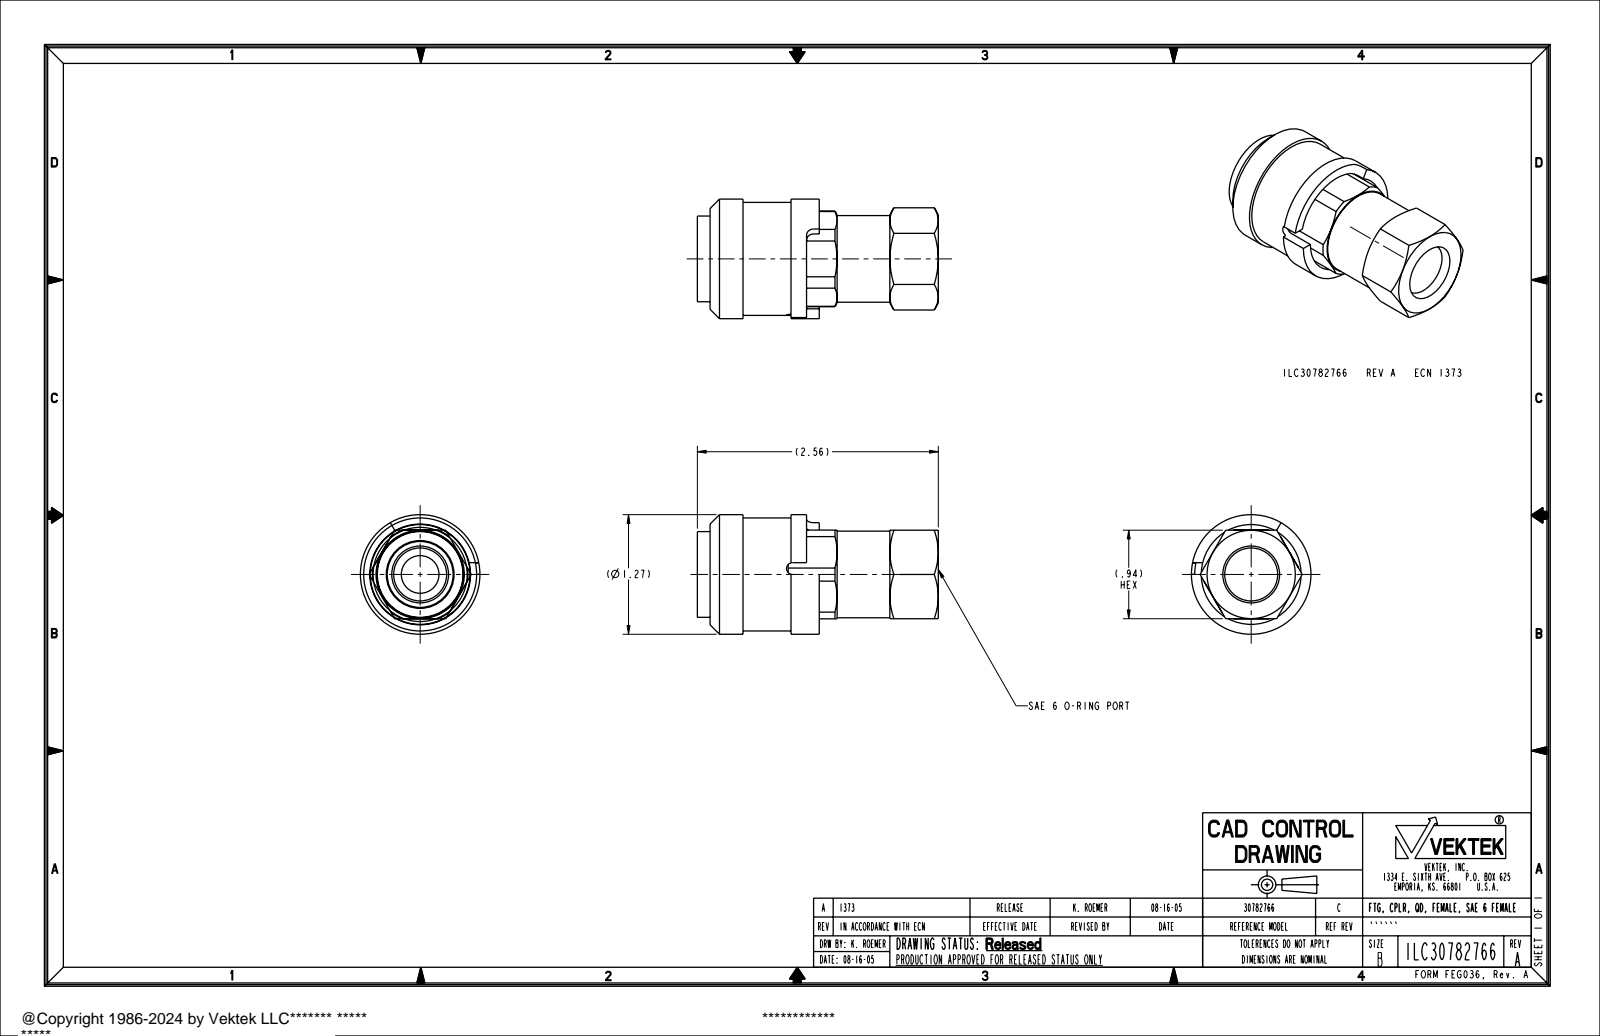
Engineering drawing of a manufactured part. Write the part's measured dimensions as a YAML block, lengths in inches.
part_name: "ILC30782766"
step_written_by: "PRO/ENGINEER BY PARAMETRIC TECHNOLOGY CORPORATION, 2004290 (AUTOMOTIVE_DESIGN_CC2)"
units: inches
bodies: {solids: 1, faces: 69, planar: 28, cylindrical: 27, other: 14}
overall_size: [2.56, 1.27, 1.27]
volume: 1.849
surface_area: 16.75
round_holes:
  - {diameter: 0.4, count: 1}
  - {diameter: 0.563, count: 1}
  - {diameter: 0.7, count: 1}
  - {diameter: 1, count: 1}
  - {diameter: 1.06, count: 1}
round_bosses_or_shafts:
  - {diameter: 1.27, count: 1}
  - {diameter: 1.2, count: 1}
  - {diameter: 0.92, count: 1}
  - {diameter: 0.91, count: 1}
partial_cylinders:
  - {radius: 0.062, count: 1}
  - {radius: 0.075, count: 1}
  - {radius: 0.508, count: 1}
face_to_face_distances: [0.94, 0.941, 0.943, 0.485, 1.265, 0.656, 0.609, 1.295, 1.951, 2.56]
